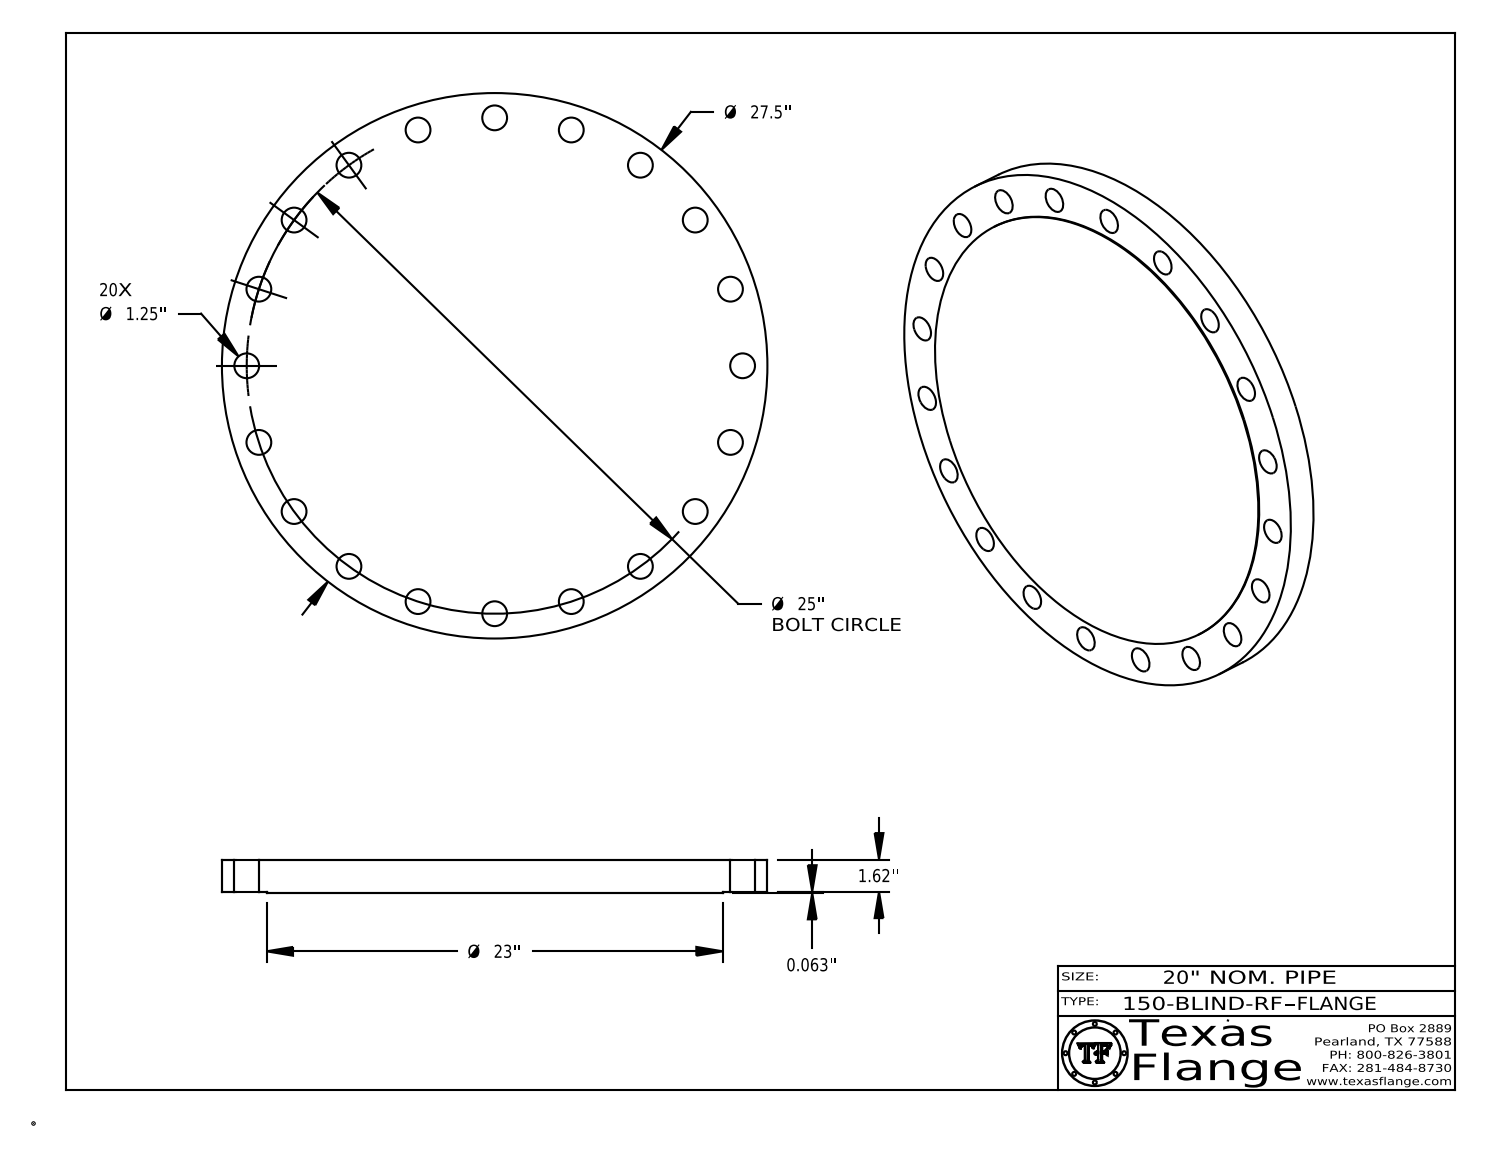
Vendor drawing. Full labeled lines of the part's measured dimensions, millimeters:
Part name (STEP PRODUCT): 150-BLIND-RF
STEP written by: CATIA V5 STEP AP214 (AUTOMOTIVE_DESIGN)
Units: millimetres
Bodies: 1 solid, 432 faces (368 planar, 64 cylindrical, 0 other)
Overall size (bounding box): 698.5 × 698.5 × 42.7
Volume: 15 540 000 mm³ · Surface area: 910 300 mm²
Round holes (diameter × count): ⌀31.8 ×20, ⌀12.6 ×1
Round bosses / shafts (diameter × count): ⌀0.8 ×8, ⌀698.5 ×1, ⌀584.2 ×1, ⌀9.9 ×1
Main face-to-face distances: 42.7, 1.6, 41.1, 42.4, 40.8, 0.4, 3.8, 3.7, 0.7, 3.1
Hole centre spacings: 373.2, 449, 513.7, 603.9, 627.2, 288.3, 565.8, 99.3
